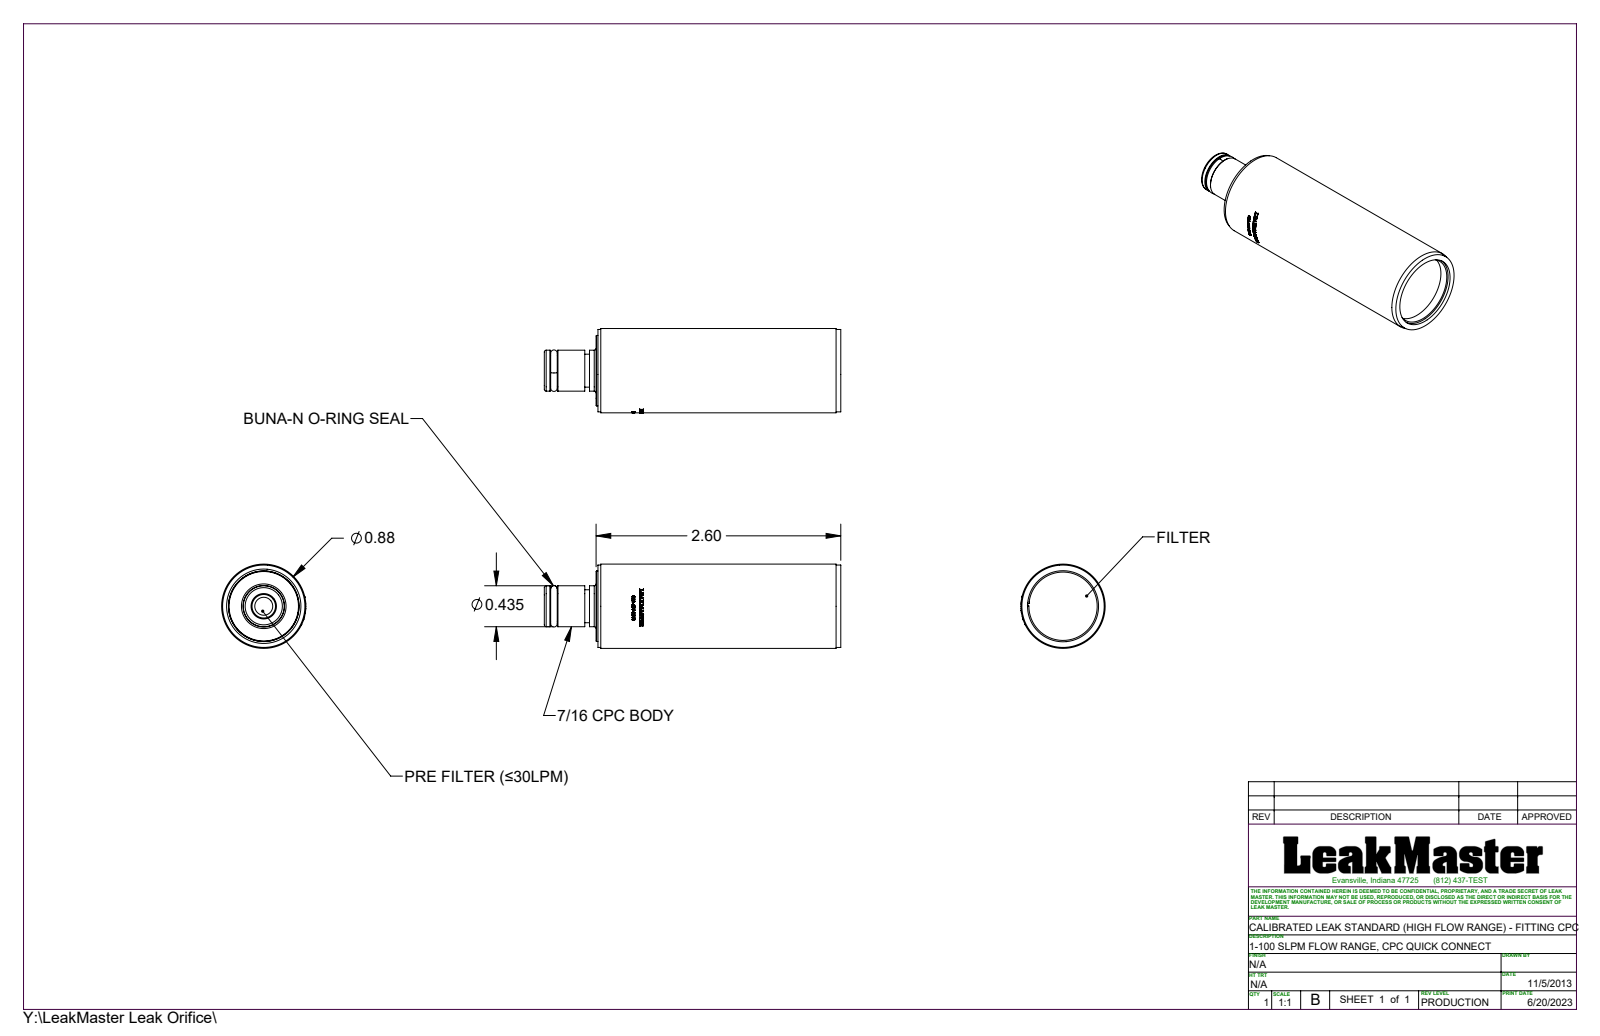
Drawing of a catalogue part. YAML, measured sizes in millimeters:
part_name: "CALIBRATED LEAK STANDARD (HIGH FLOW RANGE) - FITTING CPC"
step_written_by: "SolidWorks 2023 (CONFIG_CONTROL_DESIGN)"
units: millimeters
bodies: {solids: 6, faces: 596, planar: 228, cylindrical: 79, other: 289}
overall_size: [80, 22.7, 22.7]
volume: 12200
surface_area: 20650
round_holes:
  - {diameter: 2.3, count: 1}
  - {diameter: 4.9, count: 1}
  - {diameter: 6.4, count: 1}
  - {diameter: 16.1, count: 1}
  - {diameter: 18.4, count: 1}
  - {diameter: 19.1, count: 1}
  - {diameter: 19.2, count: 1}
  - {diameter: 19.7, count: 1}
  - {diameter: 21.7, count: 1}
round_bosses_or_shafts:
  - {diameter: 22.7, count: 1}
  - {diameter: 22.2, count: 1}
  - {diameter: 19, count: 1}
  - {diameter: 15.7, count: 1}
  - {diameter: 11, count: 1}
  - {diameter: 8.9, count: 1}
  - {diameter: 8.3, count: 1}
partial_cylinders:
  - {radius: 11.4, count: 1}
face_to_face_distances: [3.2, 1.3, 55.7, 58.9, 4.1, 59.7, 62.9, 64.8, 2.8, 58.5]
